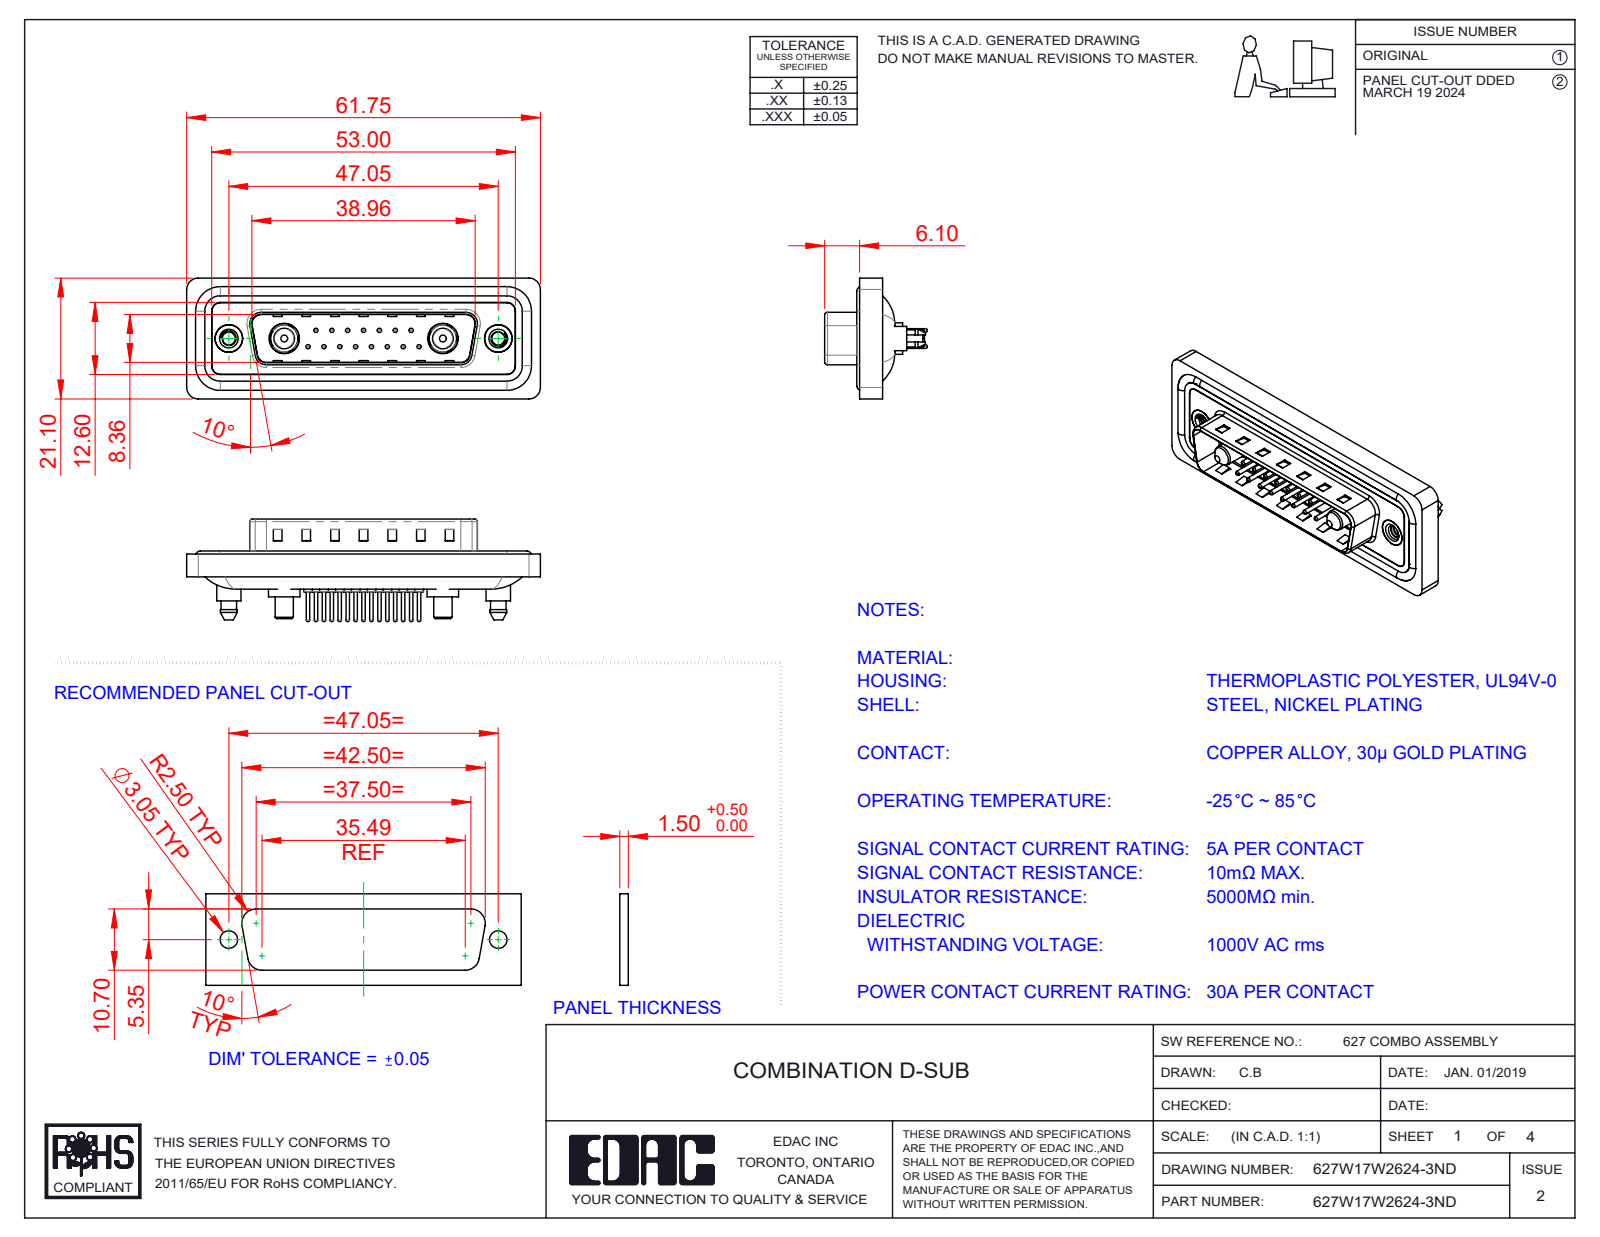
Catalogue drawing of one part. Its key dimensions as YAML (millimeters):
part_name: "627Combo Shell Rear_25 Contacts; 627Combo Shell Front_25 Contacts; 627Combo Threaded Boardlock_5; 627Combo Threaded Boardlock_D (+6 more)"
step_written_by: "SolidWorks 2023 (CONFIG_CONTROL_DESIGN)"
units: millimeters
bodies: {solids: 26, faces: 1174, planar: 350, cylindrical: 476, other: 348}
overall_size: [61.75, 21.1, 17.9]
volume: 7415
surface_area: 12259
round_holes:
  - {diameter: 0.75, count: 15}
  - {diameter: 1.6, count: 15}
  - {diameter: 2, count: 15}
  - {diameter: 2.26, count: 2}
  - {diameter: 4, count: 2}
  - {diameter: 4.8, count: 2}
  - {diameter: 4.85, count: 2}
  - {diameter: 5, count: 2}
  - {diameter: 5.3, count: 2}
round_bosses_or_shafts:
  - {diameter: 1.5, count: 15}
  - {diameter: 0.6, count: 15}
  - {diameter: 1.6, count: 4}
  - {diameter: 5.5, count: 2}
  - {diameter: 5.4, count: 2}
  - {diameter: 5.2, count: 2}
  - {diameter: 4.9, count: 2}
  - {diameter: 4.75, count: 2}
partial_cylinders:
  - {radius: 1.5, count: 24}
  - {radius: 2, count: 18}
  - {radius: 1.6, count: 10}
  - {radius: 0.5, count: 8}
  - {radius: 0.25, count: 4}
  - {radius: 0.6, count: 4}
  - {radius: 0.65, count: 4}
  - {radius: 0.9, count: 4}
face_to_face_distances: [0.4, 1.5, 1.1, 1.6, 0.5, 3.1, 2.9, 0.82, 9.58, 4.1]
hole_center_spacings: [3.16, 2.77, 5.54, 8.31, 5.04, 7.49, 11.08, 5.03]
